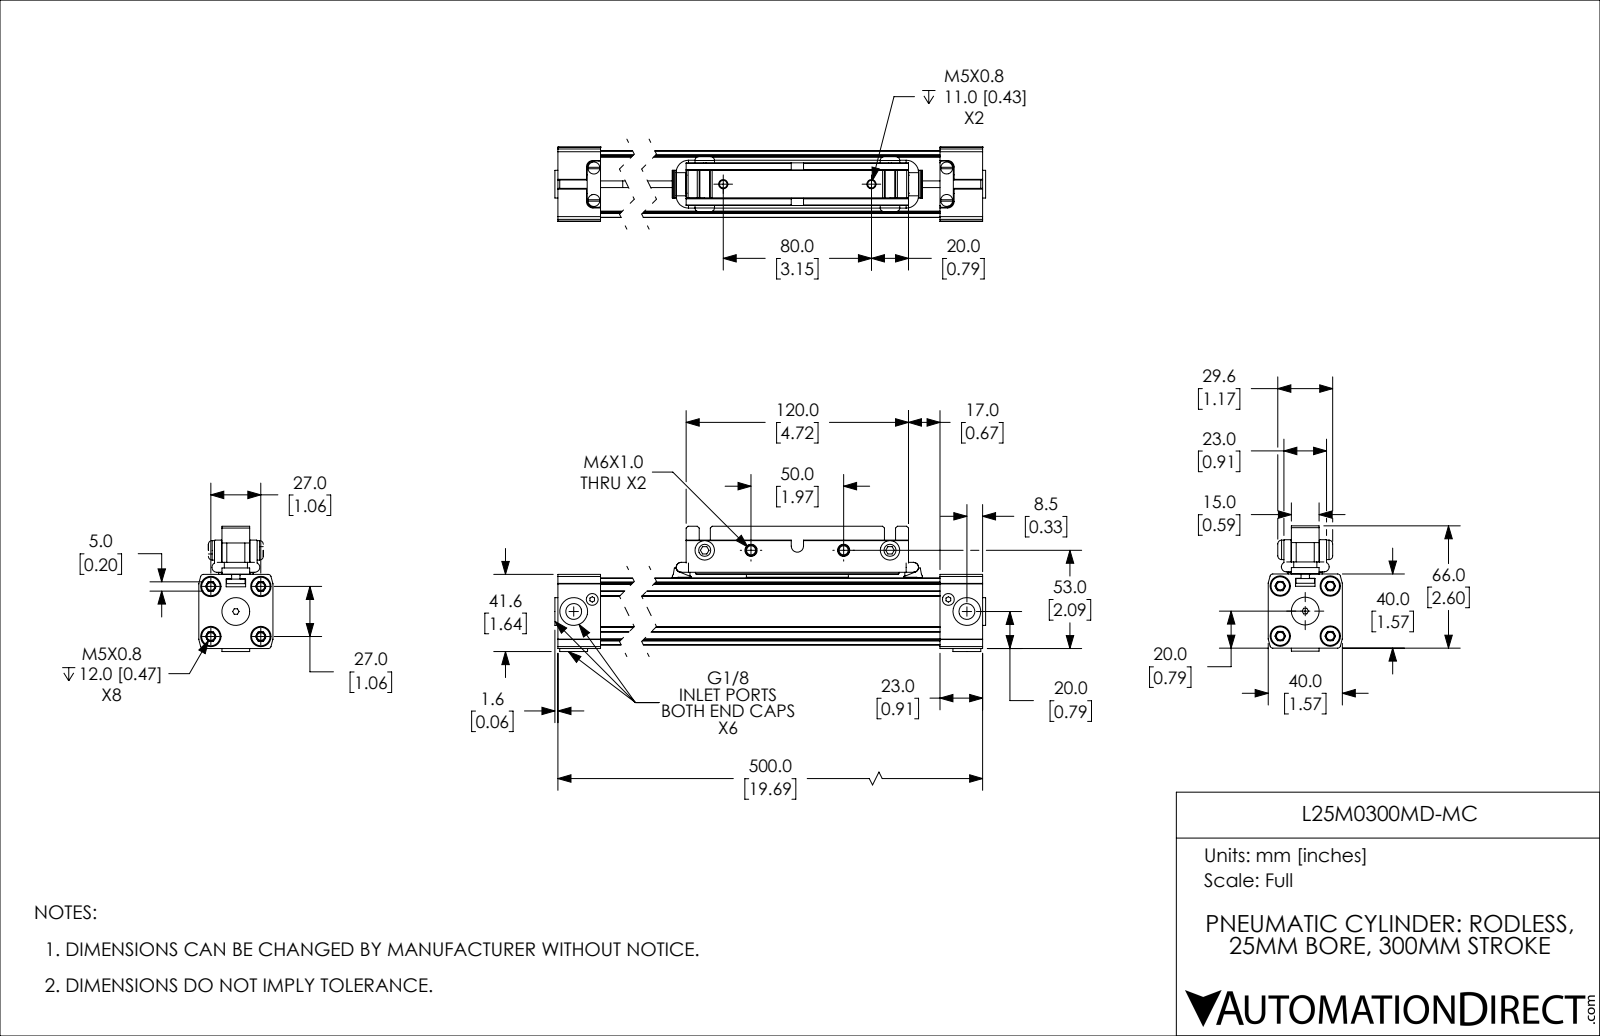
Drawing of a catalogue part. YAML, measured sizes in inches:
part_name: "L25M0300MD-MC_PISTON; L25M0300MD-MC_BODY; L25M0300MD-MC"
step_written_by: "SolidWorks 2019 (CONFIG_CONTROL_DESIGN)"
units: inches
bodies: {solids: 13, faces: 883, planar: 453, cylindrical: 322, other: 108}
overall_size: [19.814, 2.663, 1.575]
volume: 31.99
surface_area: 286.6
round_holes:
  - {diameter: 0.163, count: 6}
  - {diameter: 0.337, count: 5}
  - {diameter: 0.591, count: 5}
  - {diameter: 0.256, count: 4}
  - {diameter: 0.26, count: 4}
  - {diameter: 0.433, count: 4}
  - {diameter: 0.194, count: 2}
  - {diameter: 0.194, count: 2}
  - {diameter: 0.252, count: 2}
  - {diameter: 0.988, count: 1}
round_bosses_or_shafts:
  - {diameter: 0.394, count: 4}
  - {diameter: 0.383, count: 3}
  - {diameter: 0.323, count: 3}
  - {diameter: 0.413, count: 2}
  - {diameter: 0.21, count: 2}
  - {diameter: 0.21, count: 2}
  - {diameter: 0.984, count: 1}
partial_cylinders:
  - {radius: 0.012, count: 28}
  - {radius: 0.02, count: 14}
  - {radius: 0.039, count: 14}
  - {radius: 0.01, count: 12}
  - {radius: 0.138, count: 8}
  - {radius: 0.025, count: 6}
  - {radius: 0.059, count: 6}
  - {radius: 0.094, count: 6}
face_to_face_distances: [1.413, 1.417, 0.429, 0.079, 0.335, 0.906, 1.496, 0.717, 0.254, 1.159]
hole_center_spacings: [0.55, 0.752, 1.063, 18.59, 0.47, 0.689, 0.698, 0.809]
